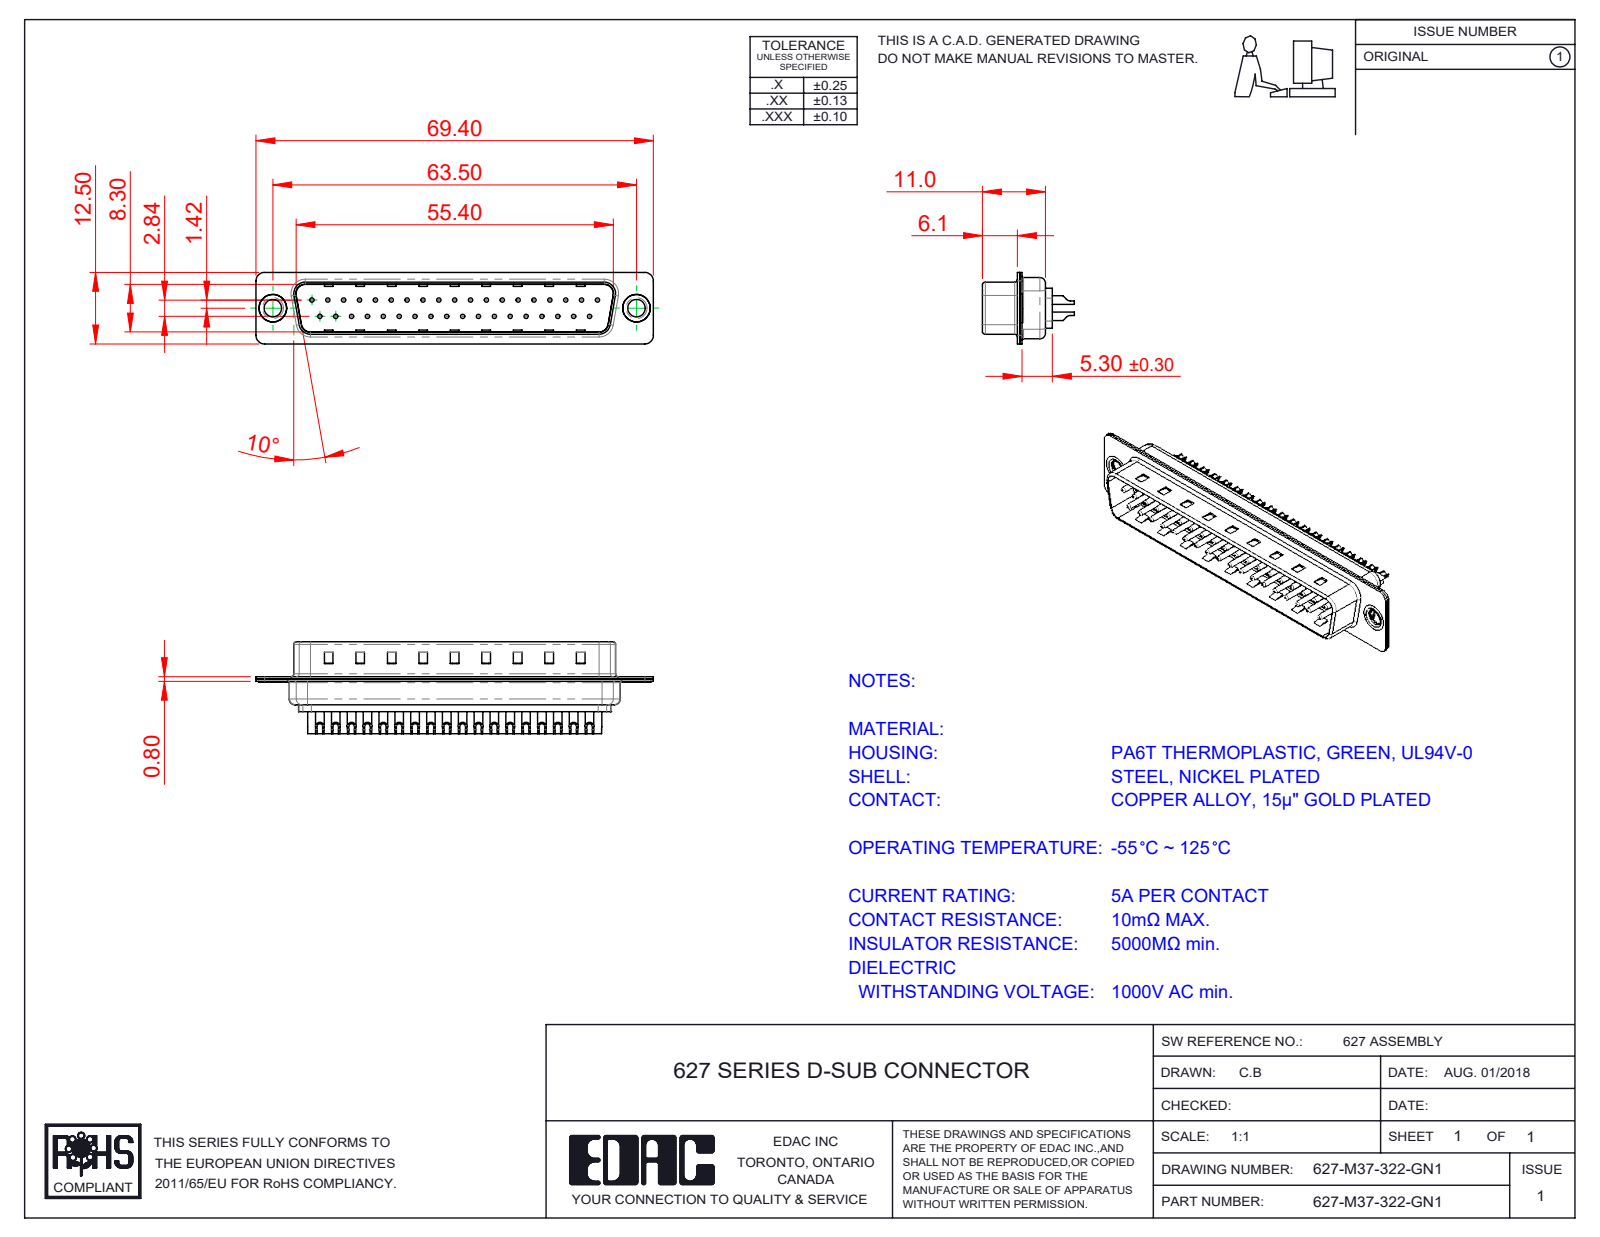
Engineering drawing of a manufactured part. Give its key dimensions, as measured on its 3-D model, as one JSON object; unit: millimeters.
{"part_name": "627M Housing_37 Contacts; 627-M37-322-GN1; 627M Thru Hole Rivet; 627M Shell Front_37 Contacts (+3 more)", "step_written_by": "SolidWorks 2020 (CONFIG_CONTROL_DESIGN)", "units": "millimeters", "bodies": {"solids": 42, "faces": 1755, "planar": 536, "cylindrical": 717, "other": 502}, "overall_size": [69.4, 16.05, 12.5], "volume_mm3": 3774, "surface_area_mm2": 9471, "round_holes": [[0.75, 37], [1, 37], [1.6, 37], [2, 37], [3.05, 2], [4, 2], [4.8, 2]], "round_bosses_or_shafts": [[1.5, 37], [5, 2], [4.9, 2], [3.55, 2]], "partial_cylinders_radius": [[1.5, 16], [2, 12], [0.5, 8], [1.6, 8], [1, 6], [0.25, 4], [0.6, 4], [0.65, 4]], "face_to_face_distances": [0.4, 0.8, 9.5, 9.1, 8.7, 9.9, 1.2, 0.75, 0.35, 5.7], "hole_center_spacings": [2.77, 5.54, 3.16, 8.31, 11.08, 13.85, 16.62, 19.39]}
